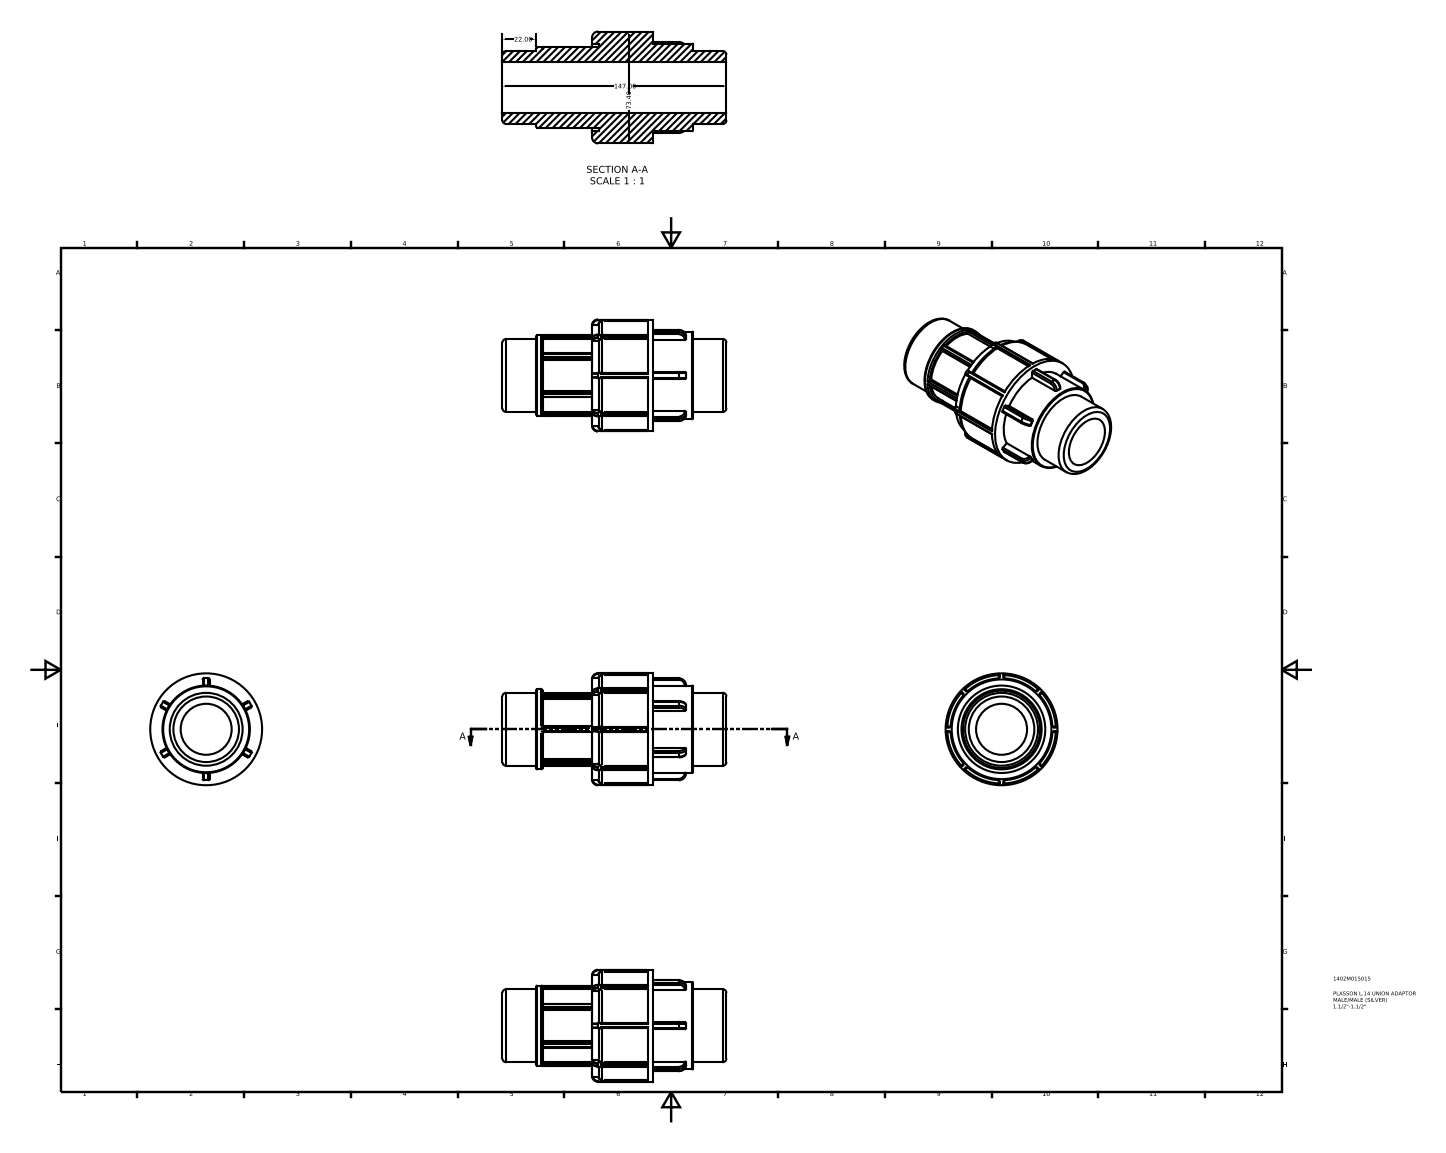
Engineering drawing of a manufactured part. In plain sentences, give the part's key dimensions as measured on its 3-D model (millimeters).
The part is named "1402M015015". Its 3-D file was written by "Autodesk Inventor 2015 (AUTOMOTIVE_DESIGN)". It is 1 solid with 250 faces: 84 planar, 108 cylindrical and 58 other. Overall it measures 147 by 73.4 by 73.4 millimeters. Its volume is 244 342 cubic millimeters and its surface area 51 904 square millimeters. Round holes: 1 of diameter 33.46, 1 of diameter 57.36. Round bosses or shafts: 1 of diameter 73.4, 1 of diameter 71.2, 1 of diameter 66.92, 1 of diameter 52.58, 1 of diameter 47.8. Partial cylindrical surfaces (rounded edges, fillets, slot ends): 32 of radius 0.37, 18 of radius 0.96, 12 of radius 1, 6 of radius 4.78. The main face-to-face distances are 4.4, 125, 22, 39.69, 35.29, 66.2, 61.8, 26.51, 58.8, 63.2.
